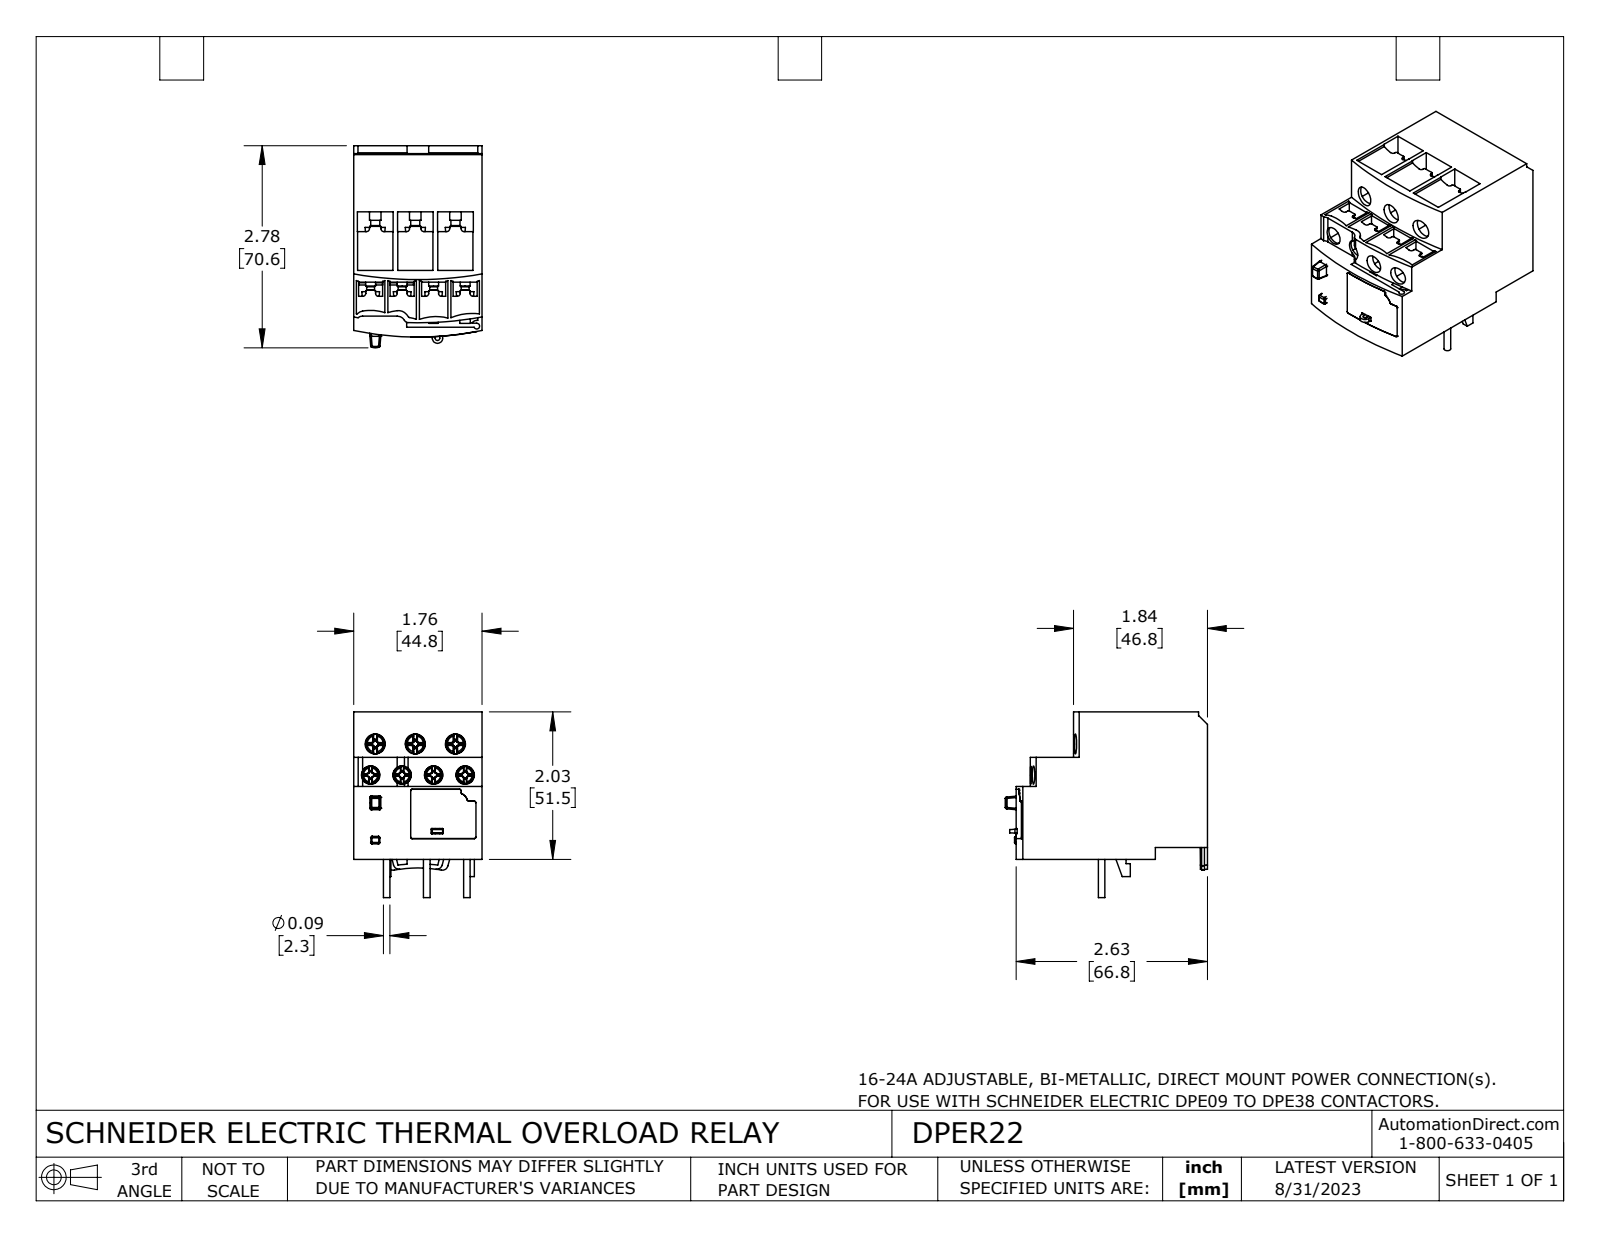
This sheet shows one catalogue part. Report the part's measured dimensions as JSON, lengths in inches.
{"part_name": "DPER22", "step_written_by": "SolidWorks 2021 (CONFIG_CONTROL_DESIGN)", "units": "inches", "bodies": {"solids": 16, "faces": 1212, "planar": 676, "cylindrical": 269, "other": 267}, "overall_size": [2.778, 2.553, 1.764], "volume_in3": 6.953, "surface_area_in2": 47.15, "round_holes": [[0.252, 4], [0.276, 3], [0.079, 2], [0.118, 2], [0.059, 1], [0.244, 1]], "round_bosses_or_shafts": [[0.091, 12], [0.138, 4], [0.108, 4], [0.157, 3], [0.154, 3], [0.124, 3], [0.118, 1], [0.107, 1]], "partial_cylinders_radius": [[0.02, 52], [0.039, 22], [0.004, 19], [0.012, 8], [0.008, 6], [0.63, 6], [0.079, 4], [0.024, 2]], "face_to_face_distances": [1.764, 0.165, 2.028, 1.863, 0.909, 0.551, 0.618, 1.409, 1.245, 2.497], "hole_center_spacings": [0.433, 0.551, 0.866, 0.334, 0.381, 0.404, 0.422, 0.449]}
